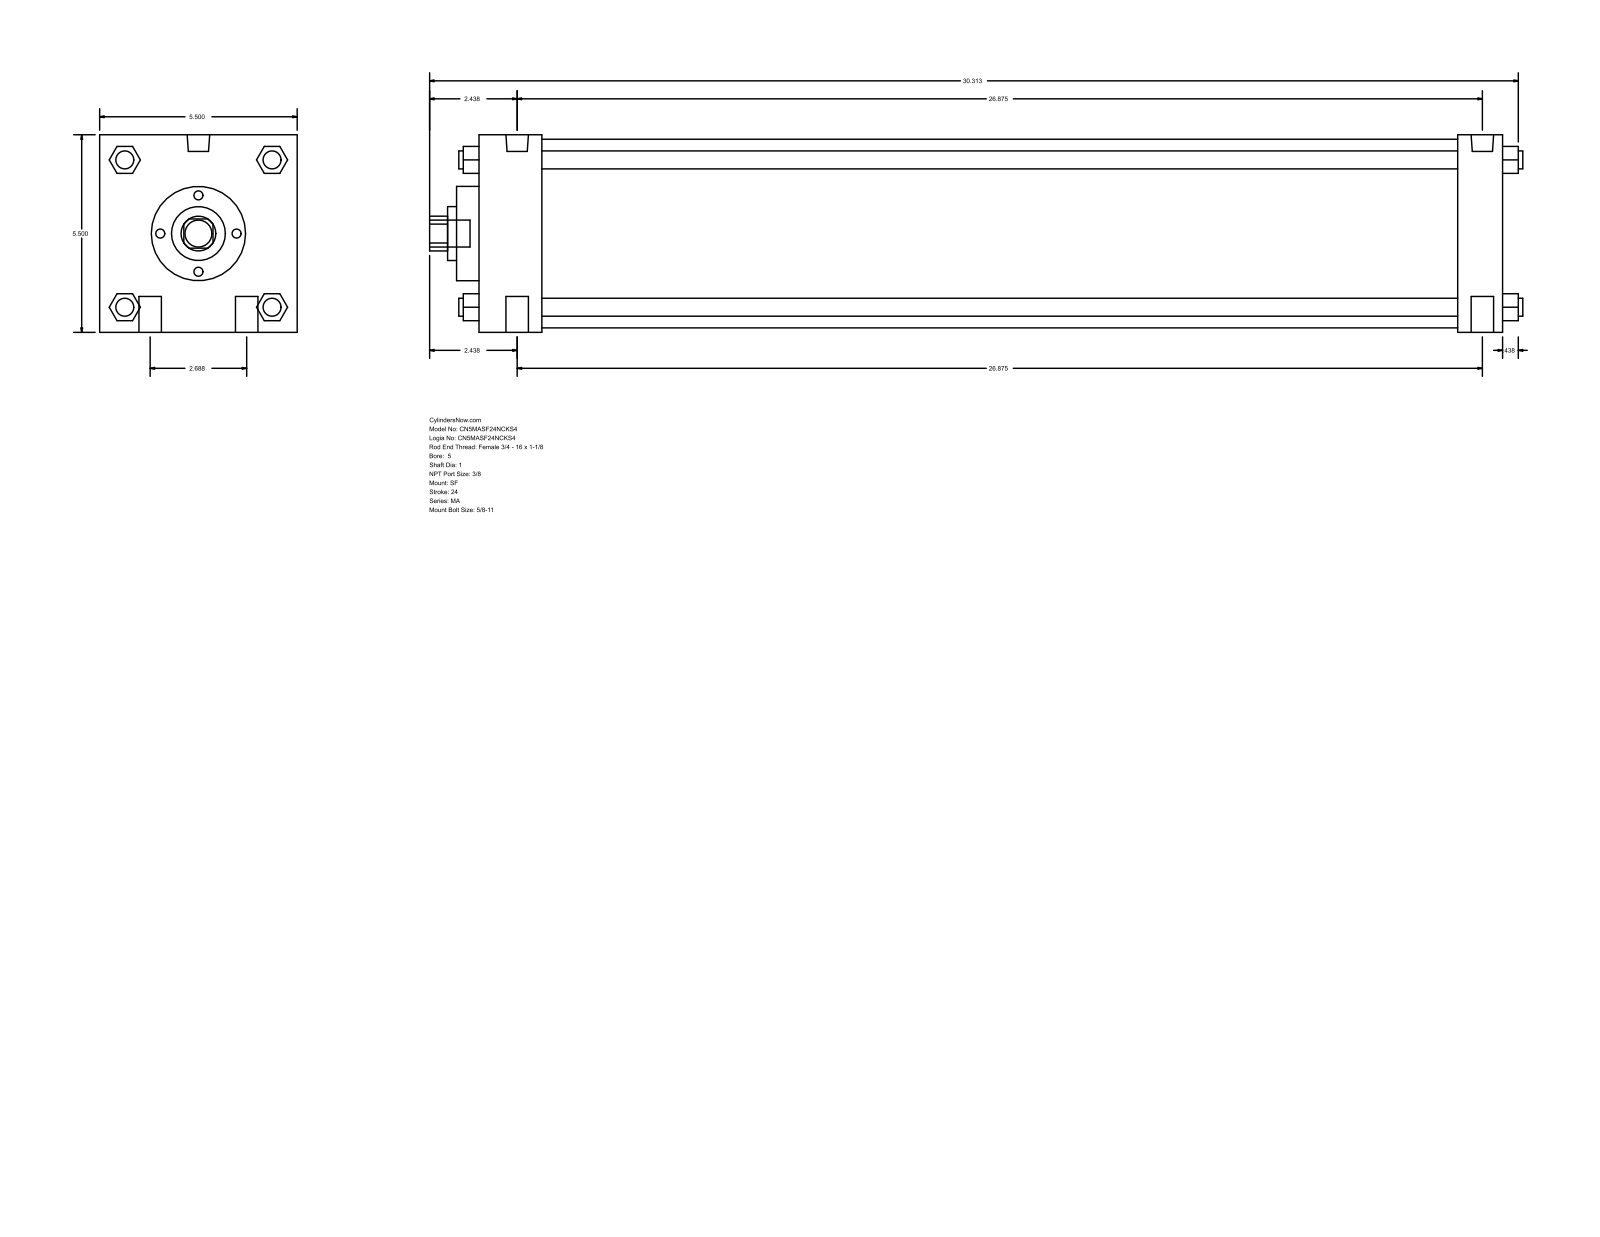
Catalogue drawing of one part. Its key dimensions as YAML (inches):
part_name: "MA_SF__0500_1"
step_written_by: "GSSL Pune (CONFIG_CONTROL_DESIGN)"
units: inches
bodies: {solids: 0, faces: 126, planar: 95, cylindrical: 31, other: 0}
overall_size: [30.437, 5.5, 5.5]
round_holes:
  - {diameter: 1, count: 1}
  - {diameter: 1.5, count: 1}
  - {diameter: 2.625, count: 1}
  - {diameter: 5.25, count: 1}
round_bosses_or_shafts:
  - {diameter: 0.625, count: 4}
  - {diameter: 0.5, count: 4}
  - {diameter: 0.627, count: 2}
  - {diameter: 0.437, count: 2}
  - {diameter: 0.75, count: 1}
partial_cylinders:
  - {radius: 0.484, count: 1}
face_to_face_distances: [5.5, 28.5, 1.75, 27.25, 25.5, 26.75, 1.25, 0.625, 2.375, 27.875]
